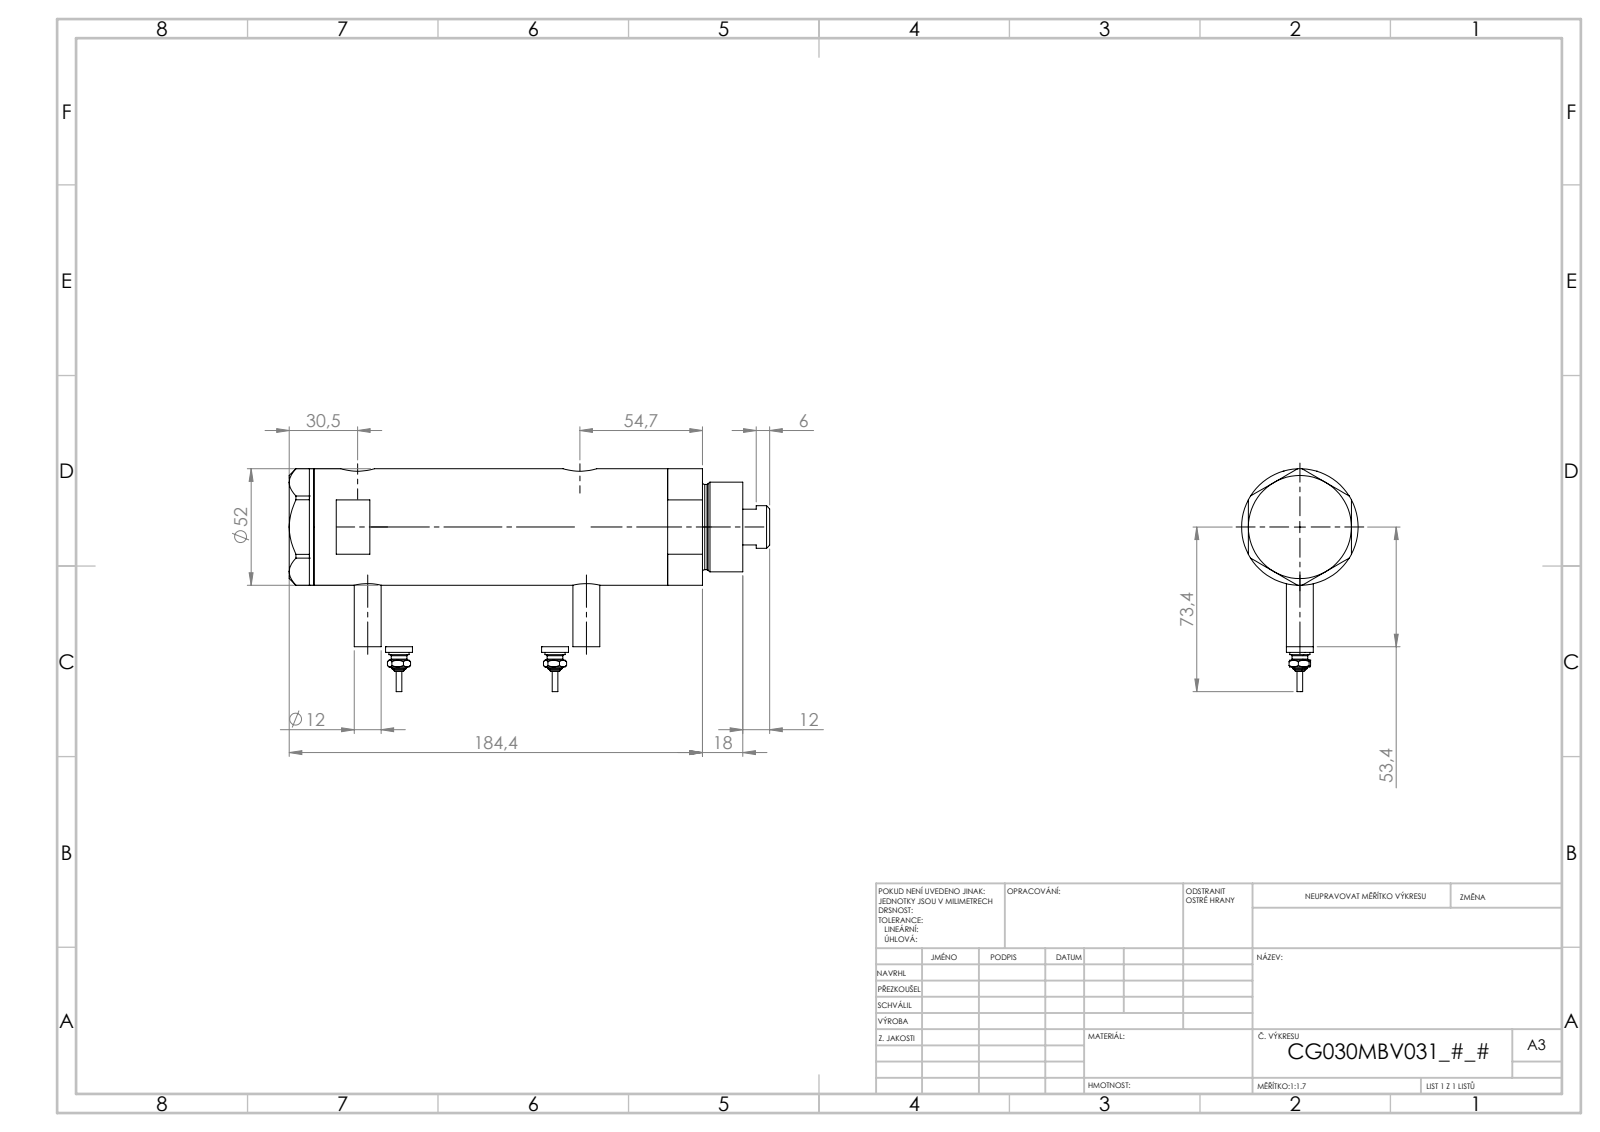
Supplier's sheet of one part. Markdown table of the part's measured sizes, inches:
| quantity | value |
| --- | --- |
| part name | V270CG_FRONT; V270CG_MIDDLE; V270CG_VC; Switch (+1 more) |
| STEP written by | SolidWorks 2019 (CONFIG_CONTROL_DESIGN) |
| units | inches |
| bodies | 6 solids, 226 faces (93 planar, 69 cylindrical, 64 other) |
| overall size | 8.441 × 3.913 × 2.047 |
| volume | 24.67 in³ |
| surface area | 140.2 in² |
| round holes (diameter × count) | 0.383 × 2, 0.492 × 2, 0.591 × 2, 0.256 × 1, 0.787 × 1, 0.846 × 1, 1.181 × 1, 1.299 × 1, 1.732 × 1 |
| round bosses / shafts (diameter × count) | 0.472 × 4, 0.354 × 2, 0.276 × 2, 0.177 × 2, 0.098 × 2, 2.047 × 1, 1.575 × 1, 1.496 × 1 |
| main face-to-face distances | 4.783, 0.937, 3.846, 0.433, 1.37, 5.217, 1.811, 1.433, 6.65, 6.217 |
| hole center spacings | 0.114, 0.177, 3.728, 3.843, 3.906, 4.02 |
